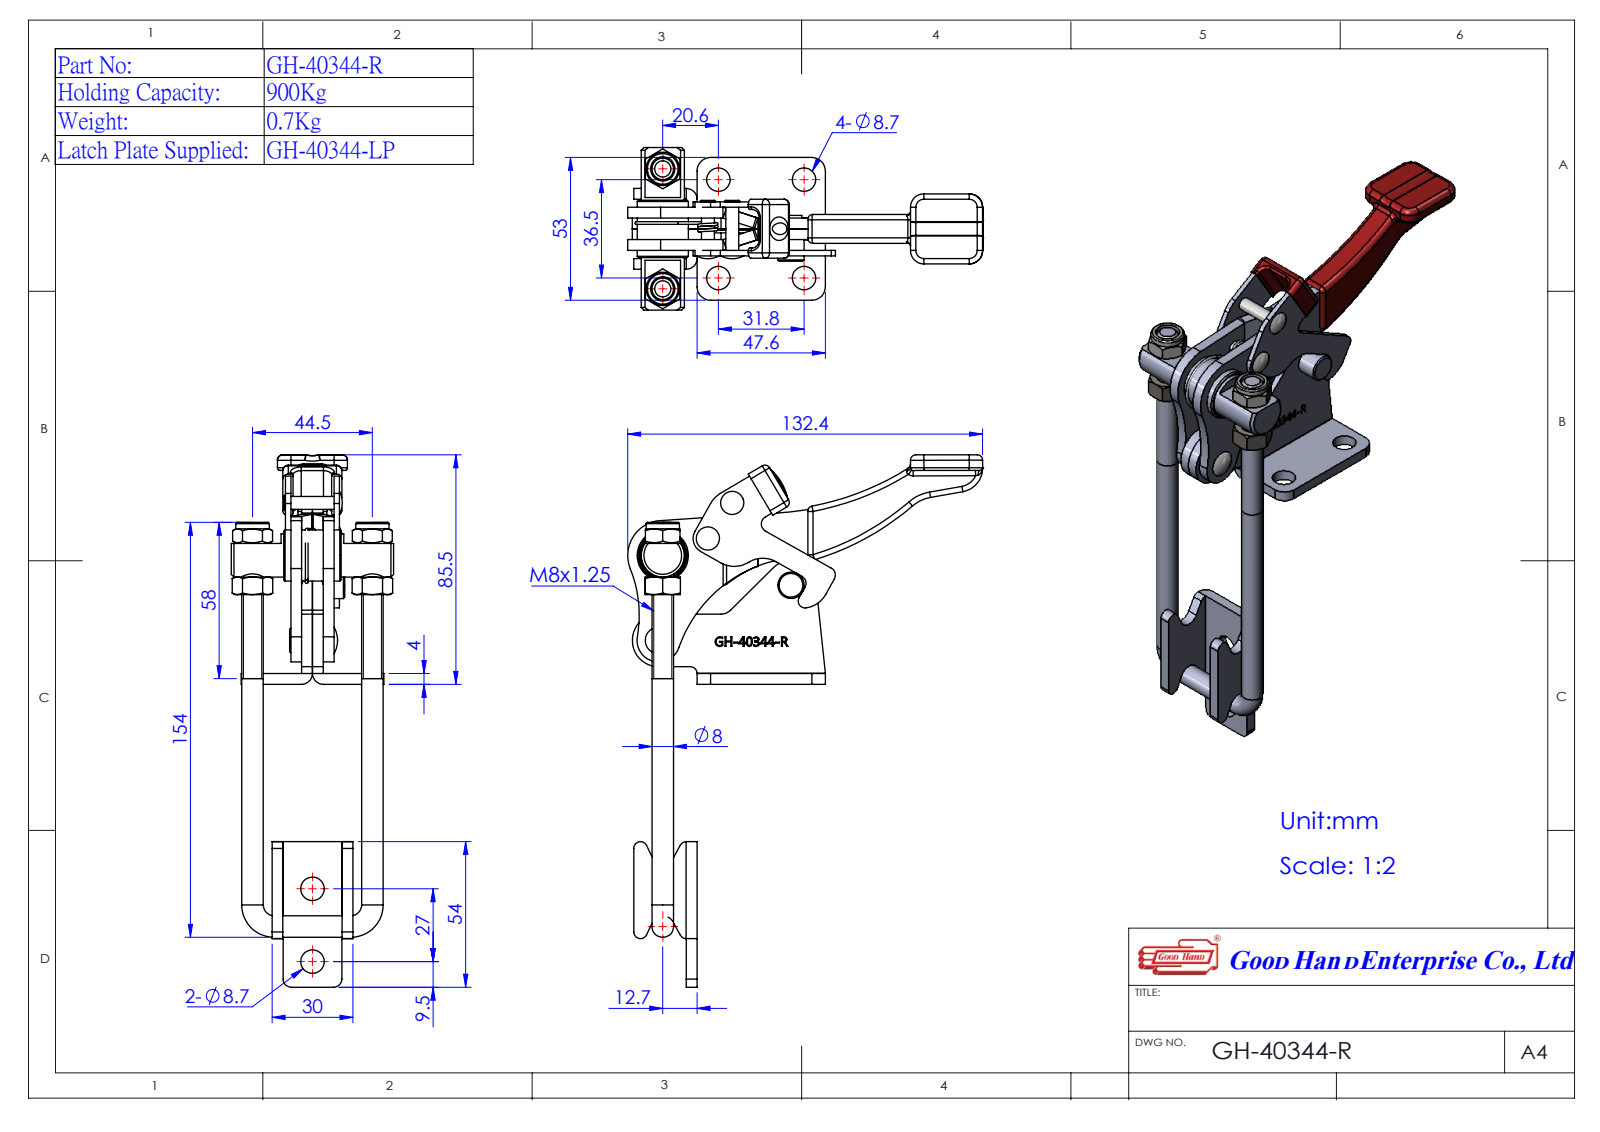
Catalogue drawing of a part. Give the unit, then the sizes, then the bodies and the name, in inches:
Units: inches
Overall size (bounding box): 7.777 × 5.187 × 2.374
Round holes (diameter × count): ⌀0.343 ×6, ⌀0.236 ×2, ⌀0.268 ×2, ⌀0.335 ×2, ⌀0.354 ×2, ⌀0.63 ×1
Round bosses / shafts (diameter × count): ⌀0.315 ×3, ⌀0.488 ×2, ⌀0.386 ×1, ⌀0.189 ×1
Partial cylindrical surfaces — rounded edges, fillets, slot ends (radius × count): R0.197 ×10, R0.004 ×8, R0.161 ×8, R0.098 ×6, R0.394 ×5, R0.118 ×3, R1.969 ×3, R0.039 ×2
Main face-to-face distances: 0.157, 0.315, 0.472, 0.748, 0.276, 0.104, 0.526, 0.053, 0.368, 0.079
Hole centre spacings: 0.828, 1.252, 1.437, 1.79, 1.906, 2.071, 2.609, 1.063
Volume: 5.9 in³ · Surface area: 76.83 in²
Bodies: 8 solids, 536 faces (262 planar, 157 cylindrical, 117 other)
Part name (STEP PRODUCT): Group5^GH-40344-R(簡化); 44034444-3^GH-40344-R(簡化); 14034414-1^GH-40344-R(簡化); Group1^GH-40344-R(簡化) (+2 more)
STEP written by: SolidWorks 2016 (AUTOMOTIVE_DESIGN)
